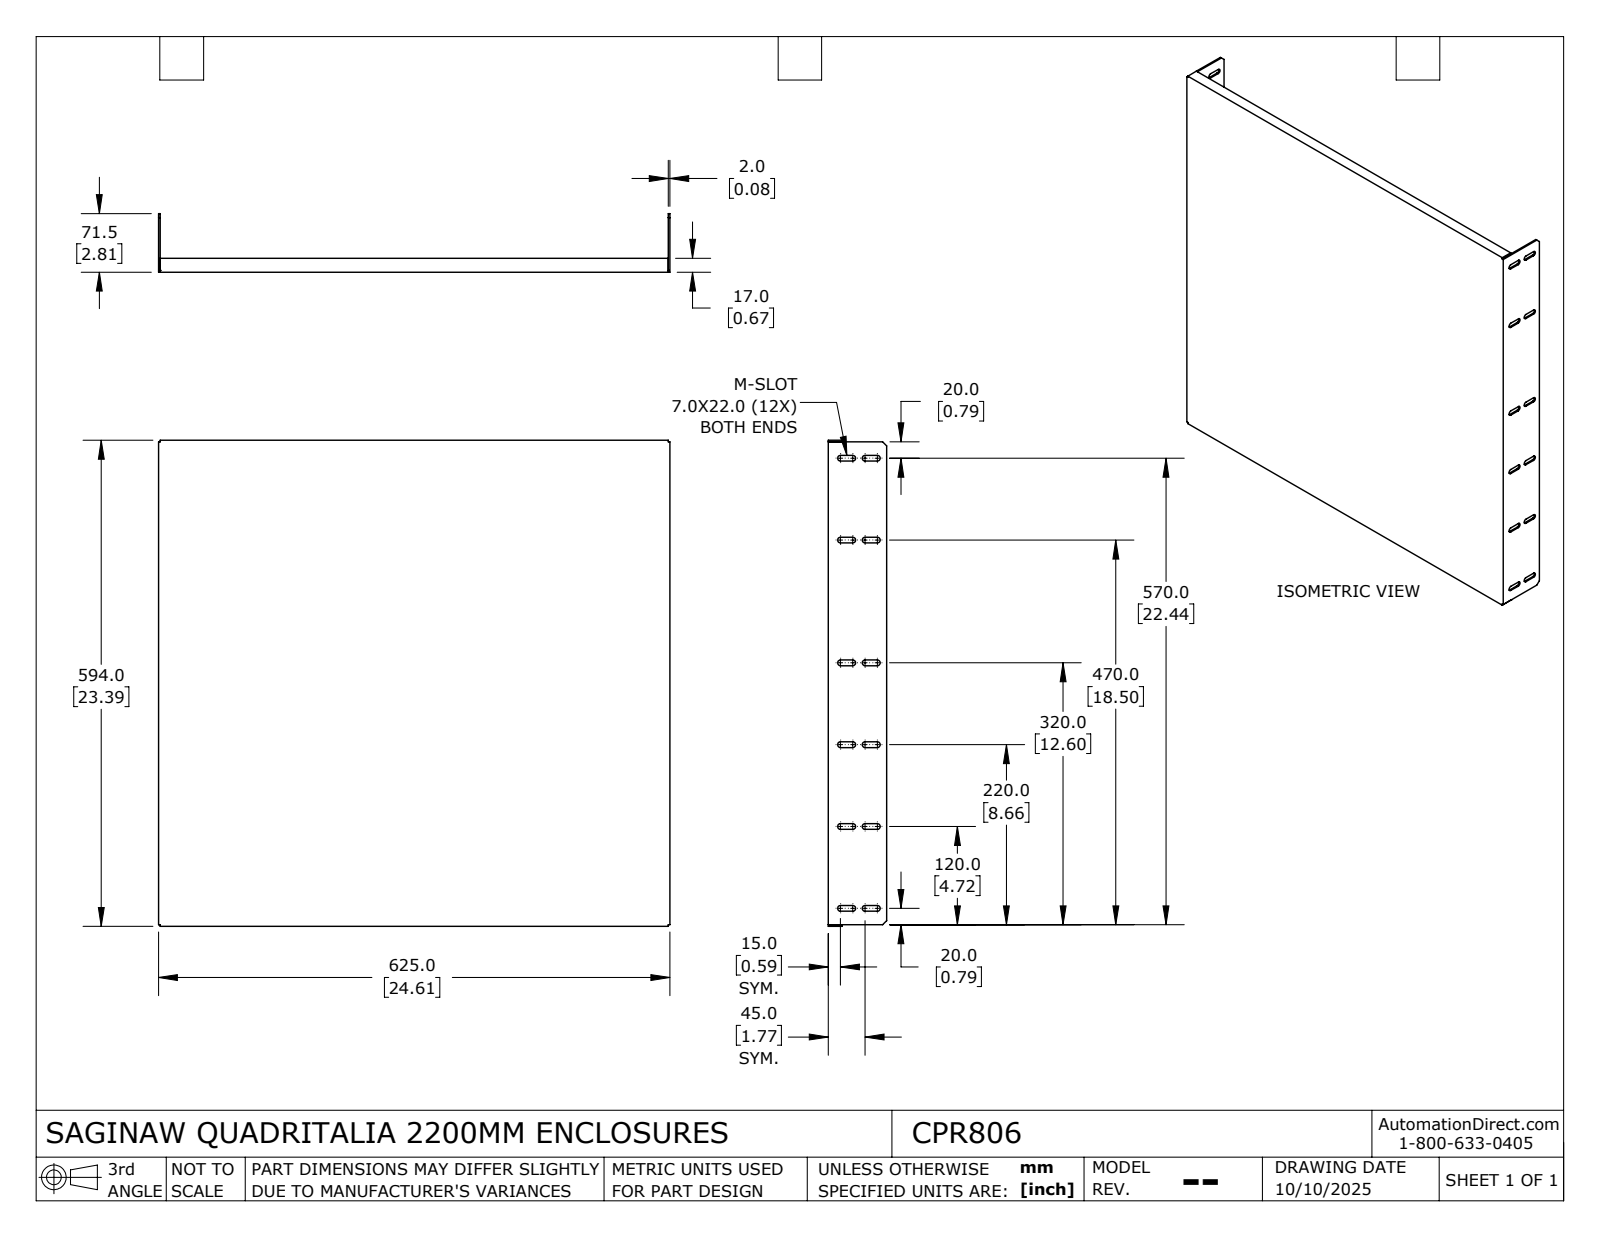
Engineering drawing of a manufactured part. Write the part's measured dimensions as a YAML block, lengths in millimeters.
part_name: "CPR806_Default"
step_written_by: "SolidWorks 2024 (CONFIG_CONTROL_DESIGN)"
units: millimeters
bodies: {solids: 1, faces: 123, planar: 75, cylindrical: 48, other: 0}
overall_size: [625, 594, 71.5]
volume: 936759
surface_area: 944784
partial_cylinders:
  - {radius: 3.5, count: 24}
face_to_face_distances: [2, 623, 625, 621, 592, 594, 590, 17, 15, 71.5]
